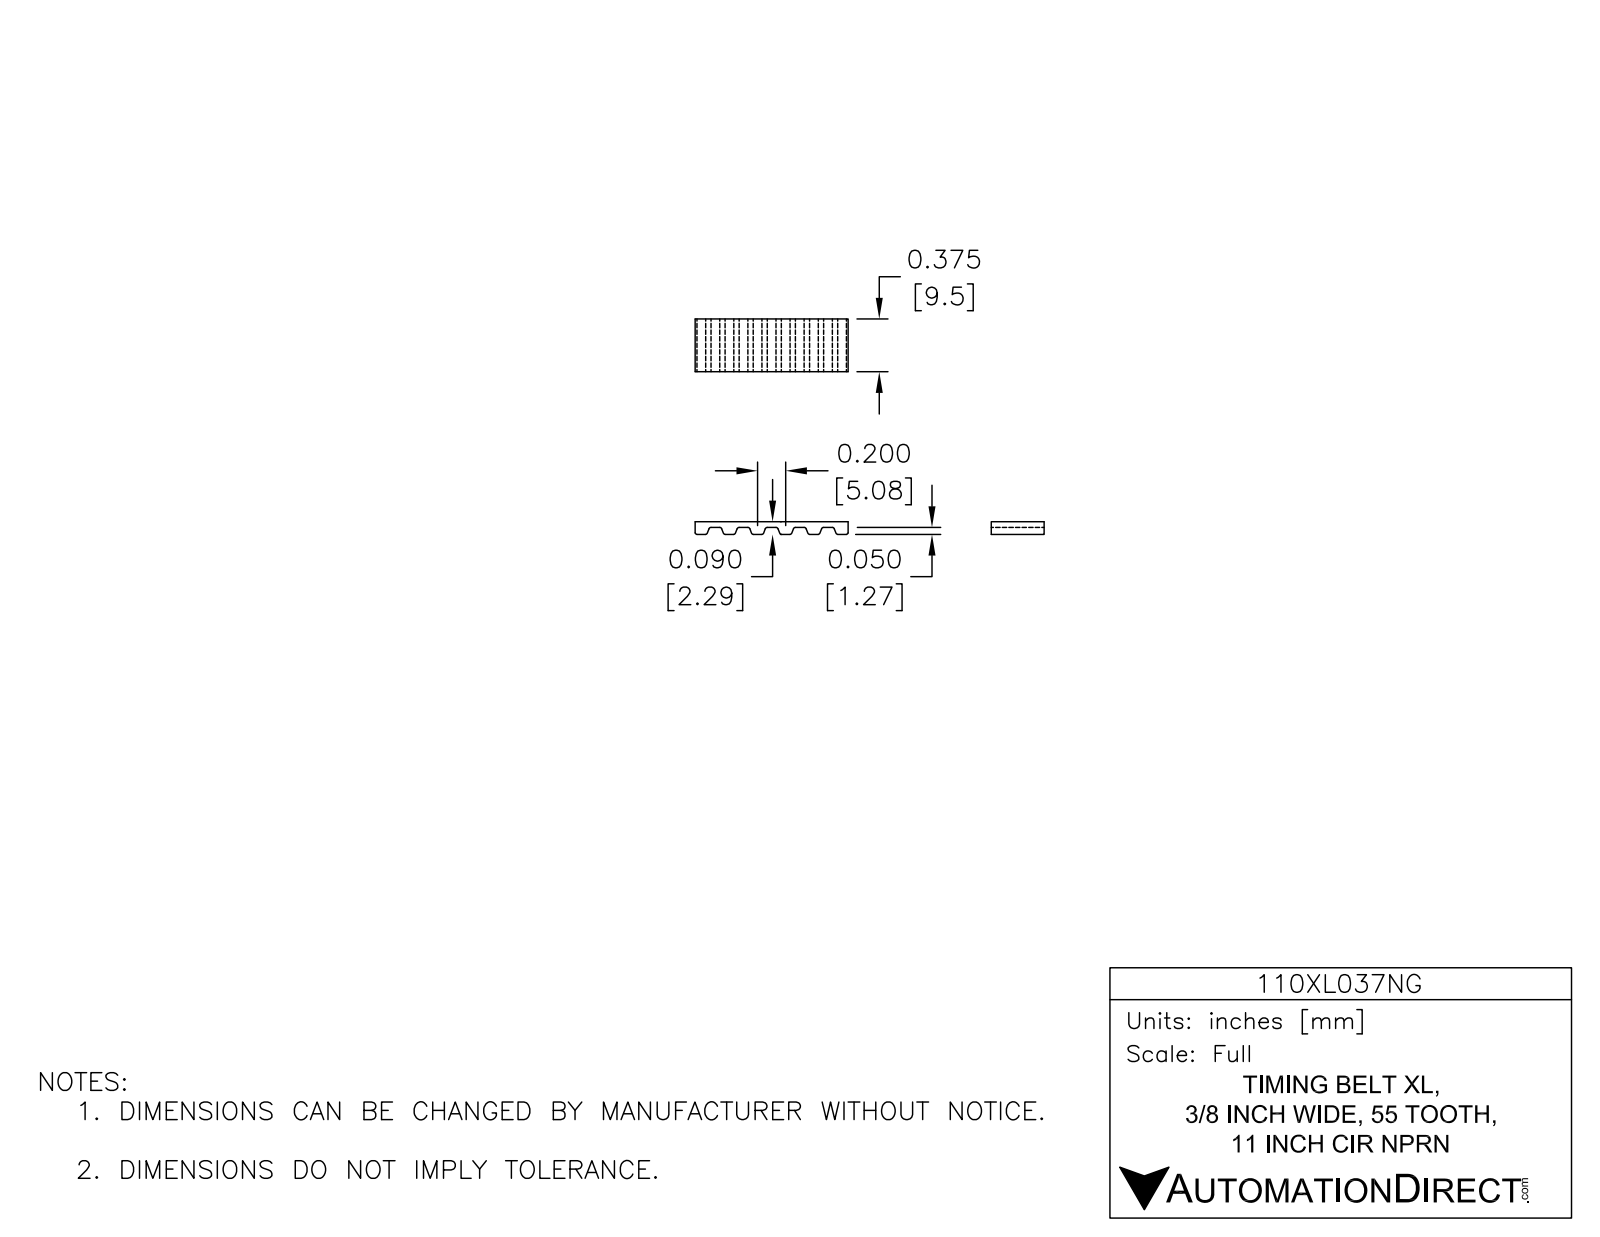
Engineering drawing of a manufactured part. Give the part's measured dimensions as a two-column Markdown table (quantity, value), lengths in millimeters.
| quantity | value |
| --- | --- |
| part name | 110XL037NG |
| STEP written by | SolidWorks 2014 (AUTOMOTIVE_DESIGN) |
| units | millimeters |
| bodies | 1 solid, 478 faces (178 planar, 300 cylindrical, 0 other) |
| overall size | 96.2 × 76.2 × 9.5 |
| volume | 3 650 mm³ |
| surface area | 6 761 mm² |
| partial cylindrical surfaces (radius × count) | 0.4 × 220, 37.1 × 2, 38.1 × 2 |
| main face-to-face distances | 9.5, 76.2, 1, 75.2, 74.2, 4.5, 27.2, 9, 22.7, 9 |
